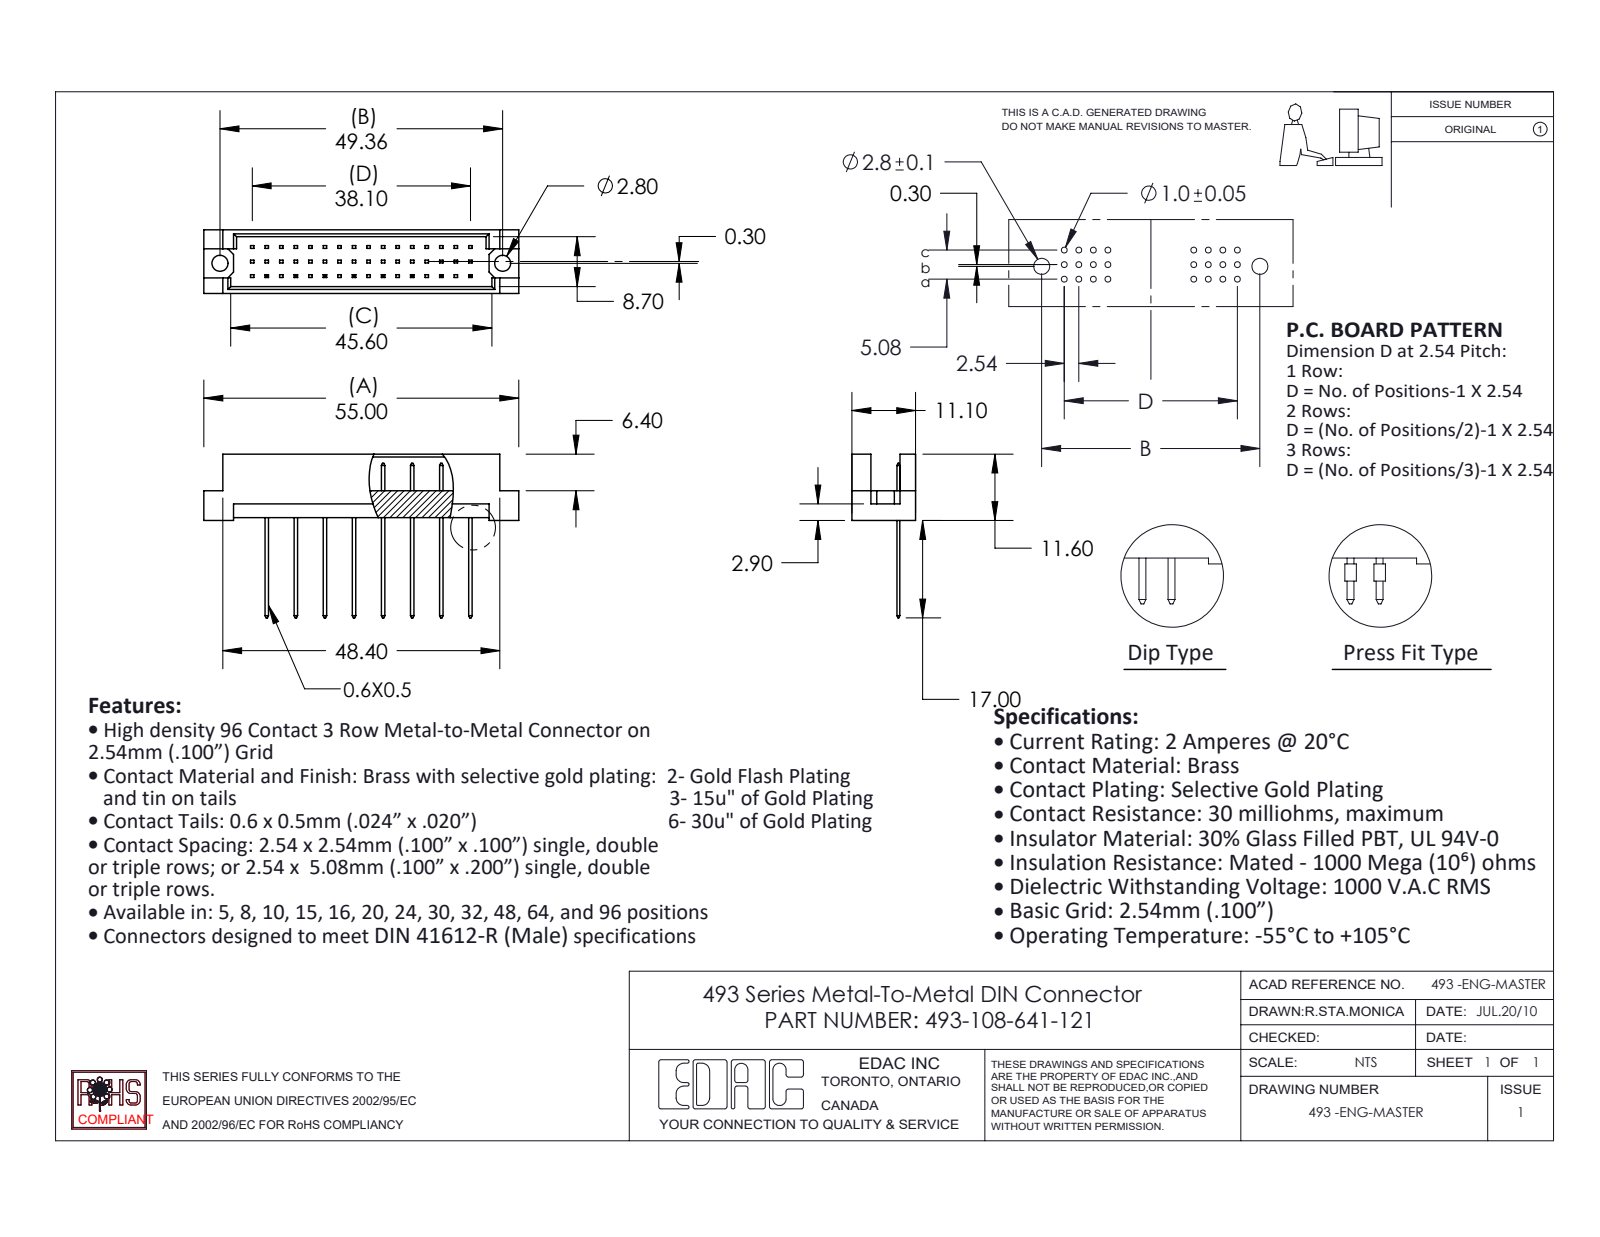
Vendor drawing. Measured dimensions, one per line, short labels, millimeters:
name: 493-290_41; 493 Part_48; 493-108-641-122
written by: SolidWorks 2020 (CONFIG_CONTROL_DESIGN)
unit: mm
bodies: 9 solids, 356 faces (352 planar, 4 cylindrical, 0 other)
size: 55 × 28.6 × 11.1
volume: 3 336 mm³; area: 4 229 mm²
holes: 2× ⌀2.8
face distances: 1.2, 9.9, 11.1, 8.7, 5.08, 4.7, 0.5, 10.16, 2.76, 8.34
hole spacings: 49.36
